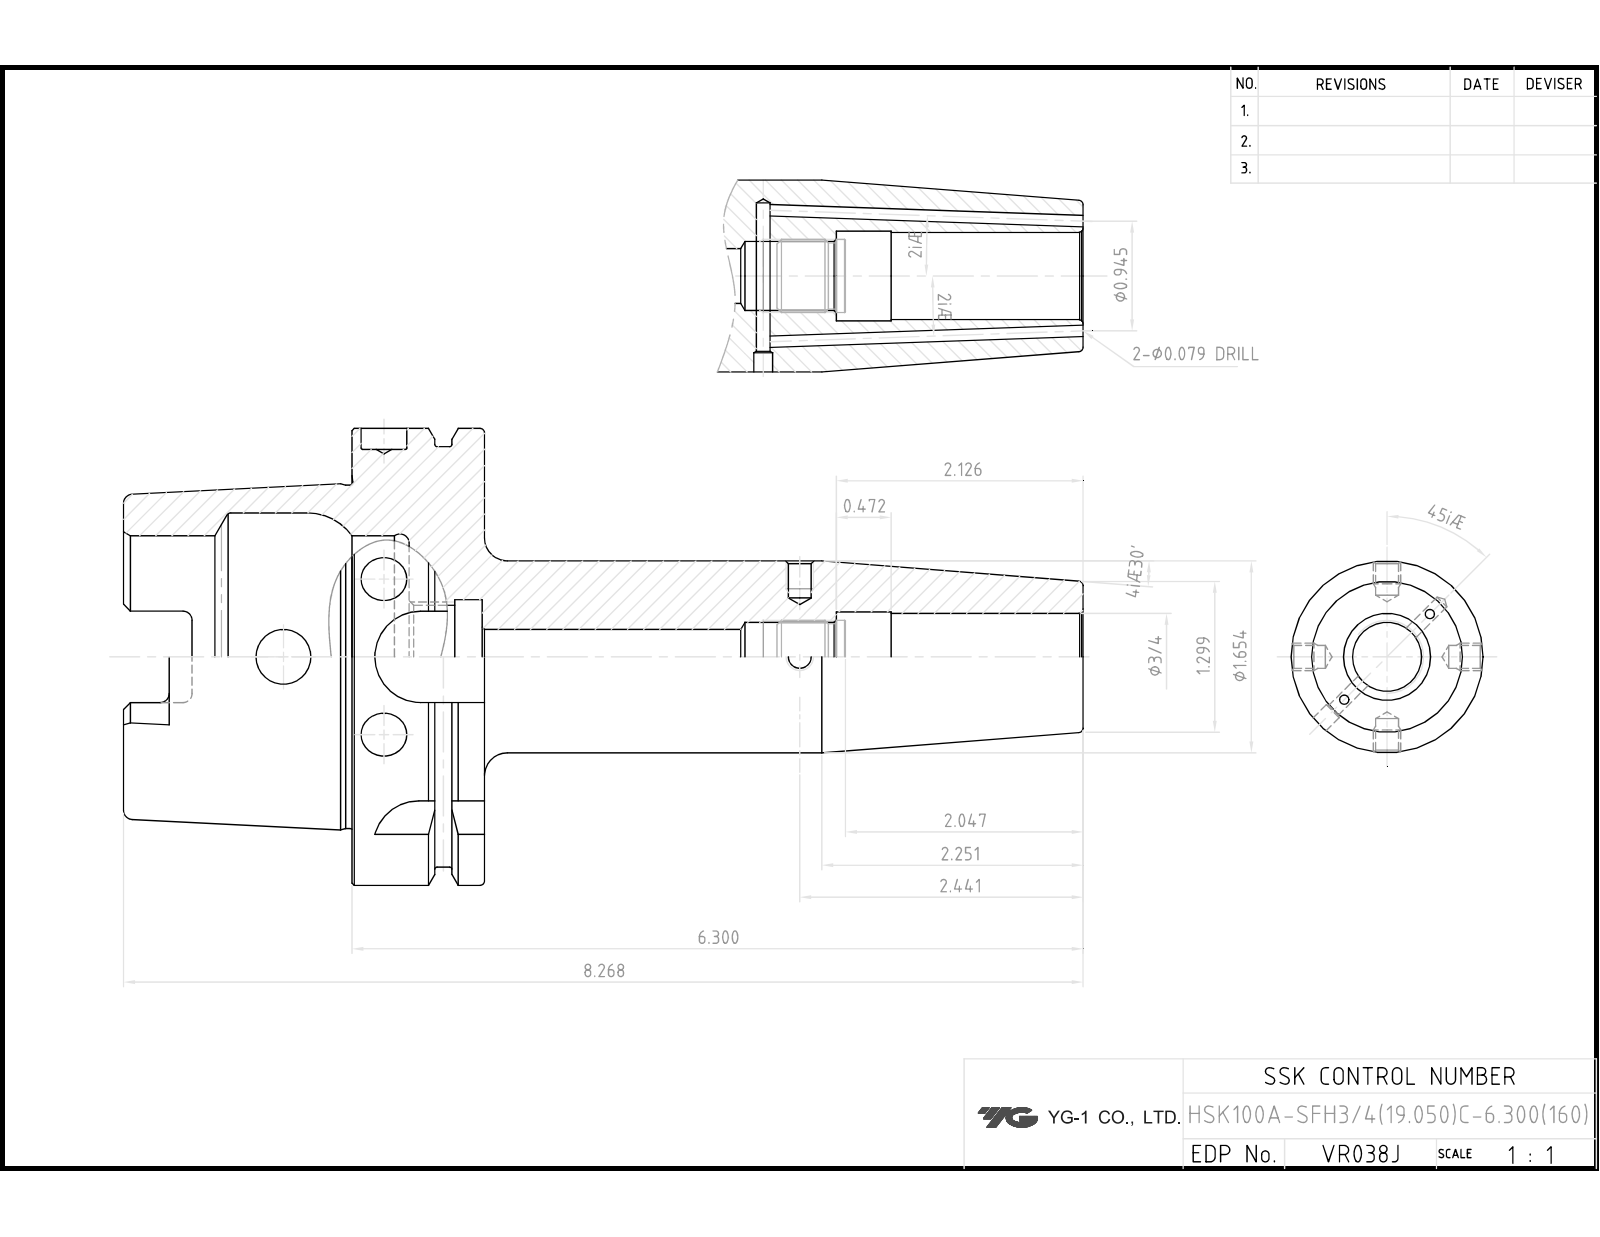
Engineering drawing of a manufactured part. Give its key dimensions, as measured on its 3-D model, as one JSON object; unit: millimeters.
{"part_name": "LO-HSK100A-SFH19.05C-160", "step_written_by": "Autodesk Inventor 2022 (AUTOMOTIVE_DESIGN)", "units": "millimeters", "bodies": {"solids": 1, "faces": 119, "planar": 38, "cylindrical": 37, "other": 44}, "overall_size": [210, 100, 100], "volume_mm3": 394274, "surface_area_mm2": 72356, "round_holes": [[2.5, 2], [12, 2], [10, 1], [14.92, 1], [19.05, 1], [20.25, 1], [22.38, 1], [25, 1], [53, 1], [63, 1]], "round_bosses_or_shafts": [[100, 1], [92, 1], [75.41, 1], [42, 1]], "partial_cylinders_radius": [[2, 6], [4.88, 4], [10, 4]], "face_to_face_distances": [29, 12.5, 16.5, 62.5, 50, 79, 210, 160, 147.5, 131]}
